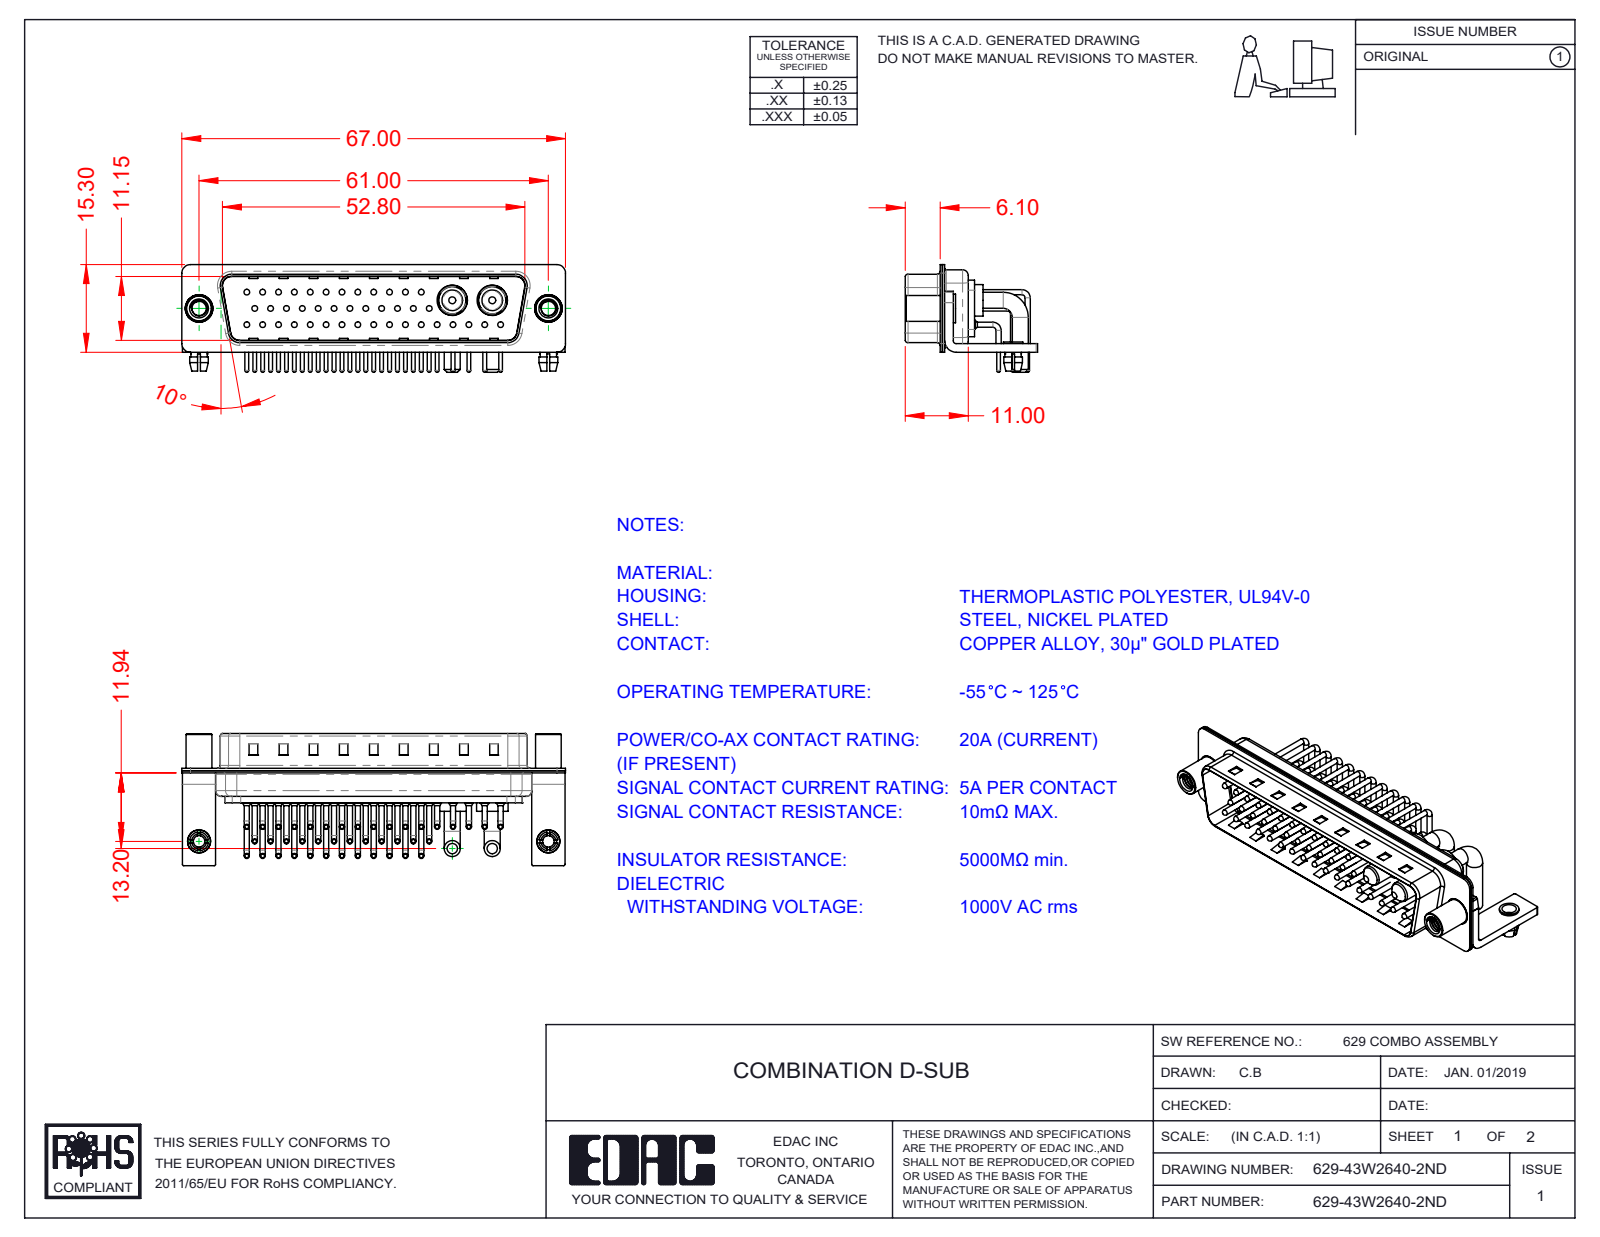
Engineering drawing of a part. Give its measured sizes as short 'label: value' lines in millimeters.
name: 629Combo Board Lock_50 Contacts; 629Combo Housing_43W2; 629Combo Stabilizer Bracket_50 Contacts; 629Combo Threaded Standoff_D (+7 more)
written by: SolidWorks 2020 (CONFIG_CONTROL_DESIGN)
unit: mm
bodies: 54 solids, 5198 faces (2917 planar, 1763 cylindrical, 518 other)
size: 67 × 23.1 × 18.8
volume: 5 700 mm³; area: 13 836 mm²
holes: 43× ⌀2, 41× ⌀0.75, 41× ⌀1.6, 4× ⌀2.5, 2× ⌀3.2, 2× ⌀4, 2× ⌀4.8, 2× ⌀4.85, 2× ⌀5.3
bosses: 82× ⌀0.9, 41× ⌀1.5, 41× ⌀1, 41× ⌀0.65, 4× ⌀2.8, 2× ⌀5.5, 2× ⌀5.2, 2× ⌀5
rounds: 41× R1.01, 16× R0.25, 16× R1.5, 13× R2, 9× R0.5, 8× R1.6, 4× R0.6, 4× R0.65
face distances: 0.4, 1.5, 11.55, 5.6, 5.2, 0.8, 1.9, 4.1, 6, 0.78
hole spacings: 2.77, 5.54, 3.16, 8.31, 11.08, 13.85, 16.62, 19.39
